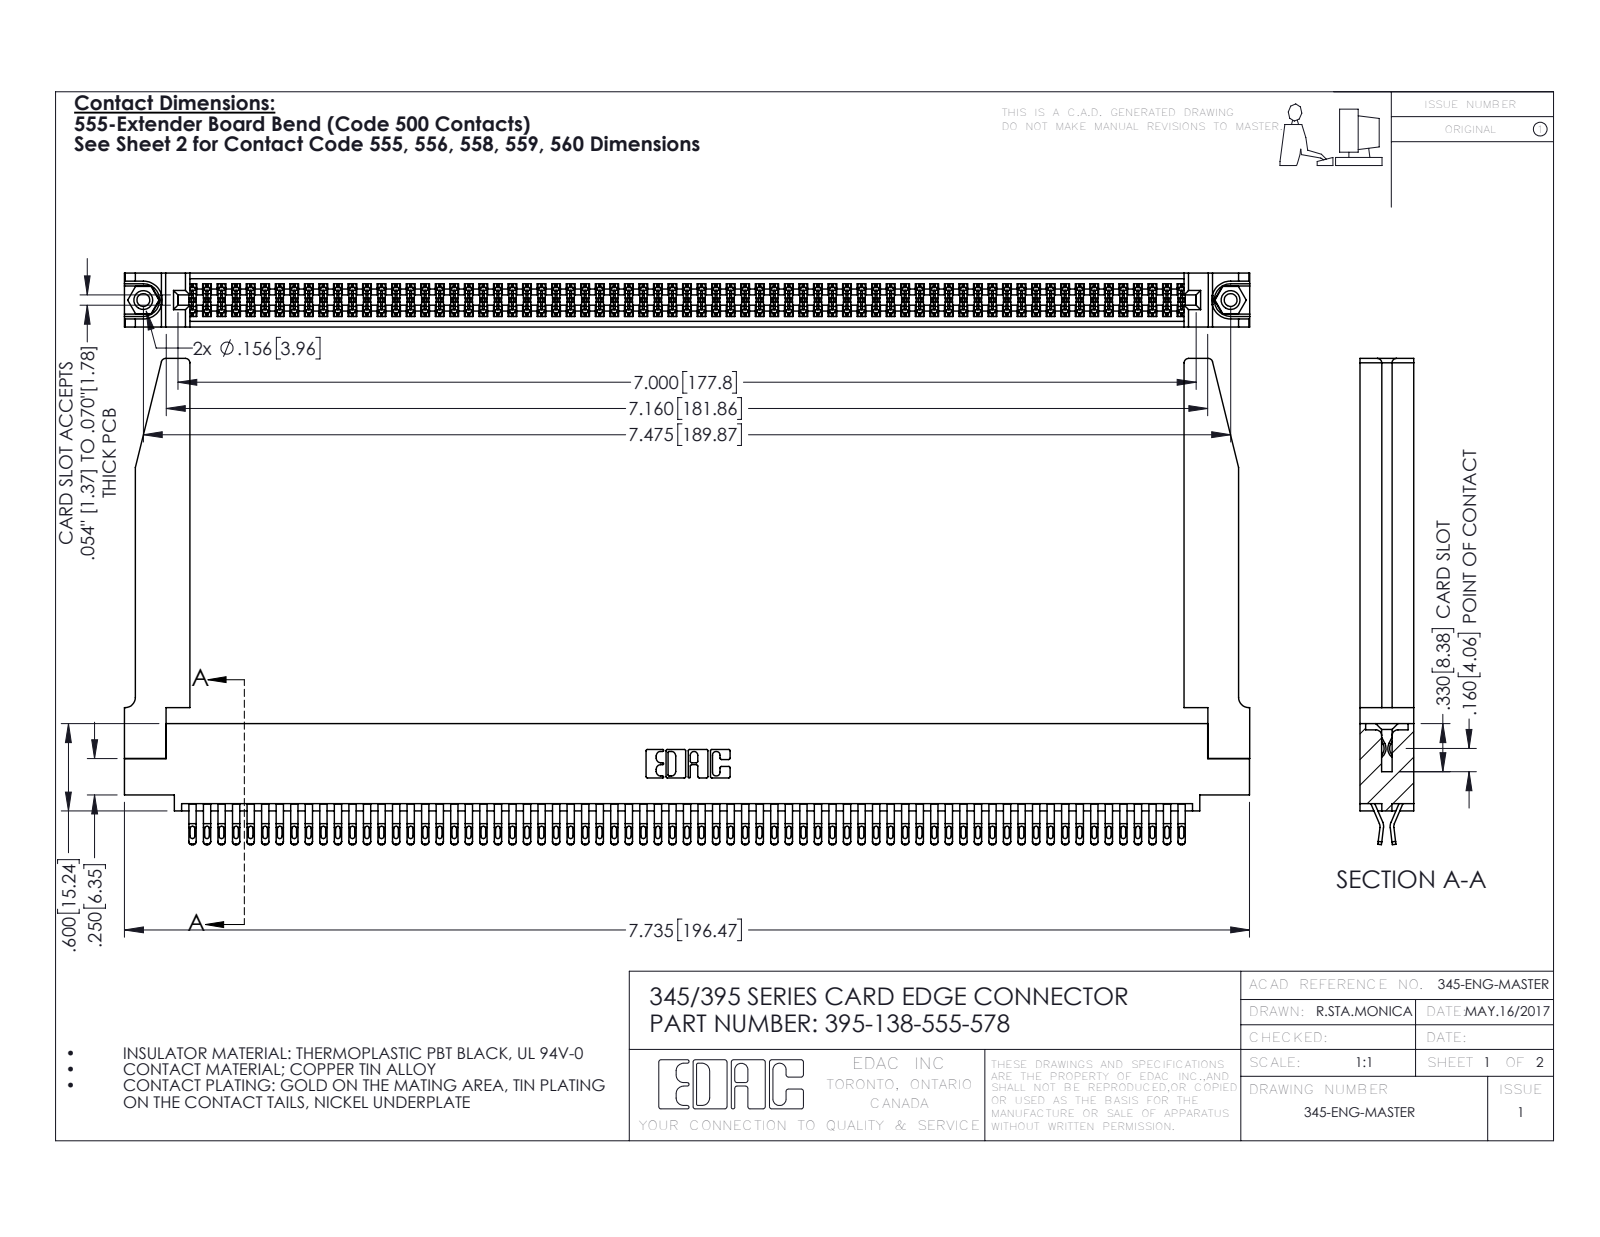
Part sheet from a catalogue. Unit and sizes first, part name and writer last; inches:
Units: inches
Overall size (bounding box): 7.736 × 3.342 × 0.37
Round holes (diameter × count): ⌀0.089 ×2, ⌀0.125 ×2, ⌀0.156 ×2, ⌀0.064 ×1
Round bosses / shafts (diameter × count): ⌀0.155 ×2
Partial cylindrical surfaces — rounded edges, fillets, slot ends (radius × count): R0.016 ×345, R0.02 ×276, R0.006 ×207, R0.01 ×22, R0.03 ×8, R0.007 ×6, R0.031 ×6, R0.026 ×3
Main face-to-face distances: 0.072, 0.298, 0.37, 0.025, 0.098, 0.272, 0.2, 0.225, 0.175, 0.149
Hole centre spacings: 0.27, 7.239, 7.475
Volume: 1.674 in³ · Surface area: 58.77 in²
Bodies: 143 solids, 8092 faces (4504 planar, 3536 cylindrical, 52 other)
Part name (STEP PRODUCT): 345-250-001_345-250-001-102; 395-138-555-578; 345-220-078_345-220-078; 345-292-001_555 Tail (+1 more)
STEP written by: SolidWorks 2016 (CONFIG_CONTROL_DESIGN)
